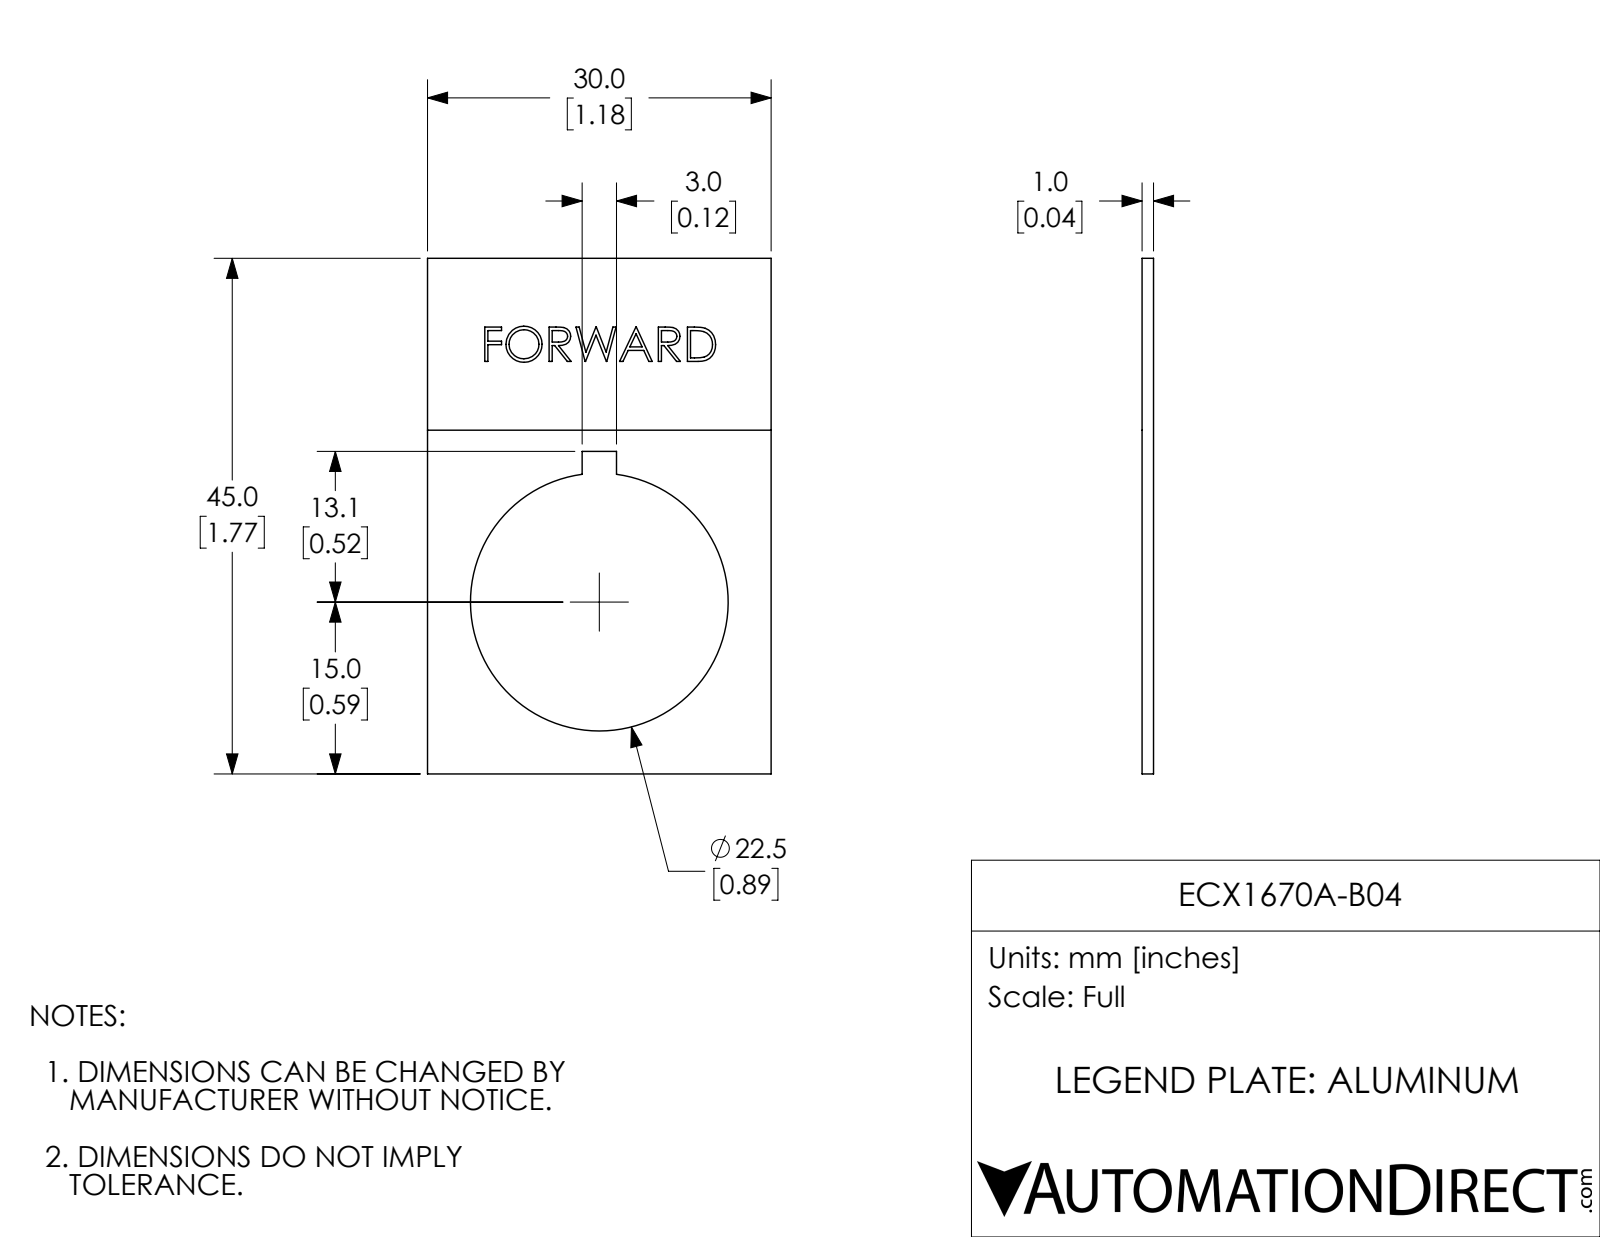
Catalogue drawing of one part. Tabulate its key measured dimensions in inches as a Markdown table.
| quantity | value |
| --- | --- |
| part name | ECX1670A-B04 |
| STEP written by | SolidWorks 2017 (AUTOMOTIVE_DESIGN) |
| units | inches |
| bodies | 1 solid, 112 faces (84 planar, 3 cylindrical, 25 other) |
| overall size | 1.772 × 1.181 × 0.039 |
| volume | 0.058 in³ |
| surface area | 3.287 in² |
| round holes (diameter × count) | 0.886 × 1 |
| main face-to-face distances | 0.039, 1.181, 1.772, 0.038, 0.65, 0.531, 1.108, 0.663, 0.118, 0.221 |
